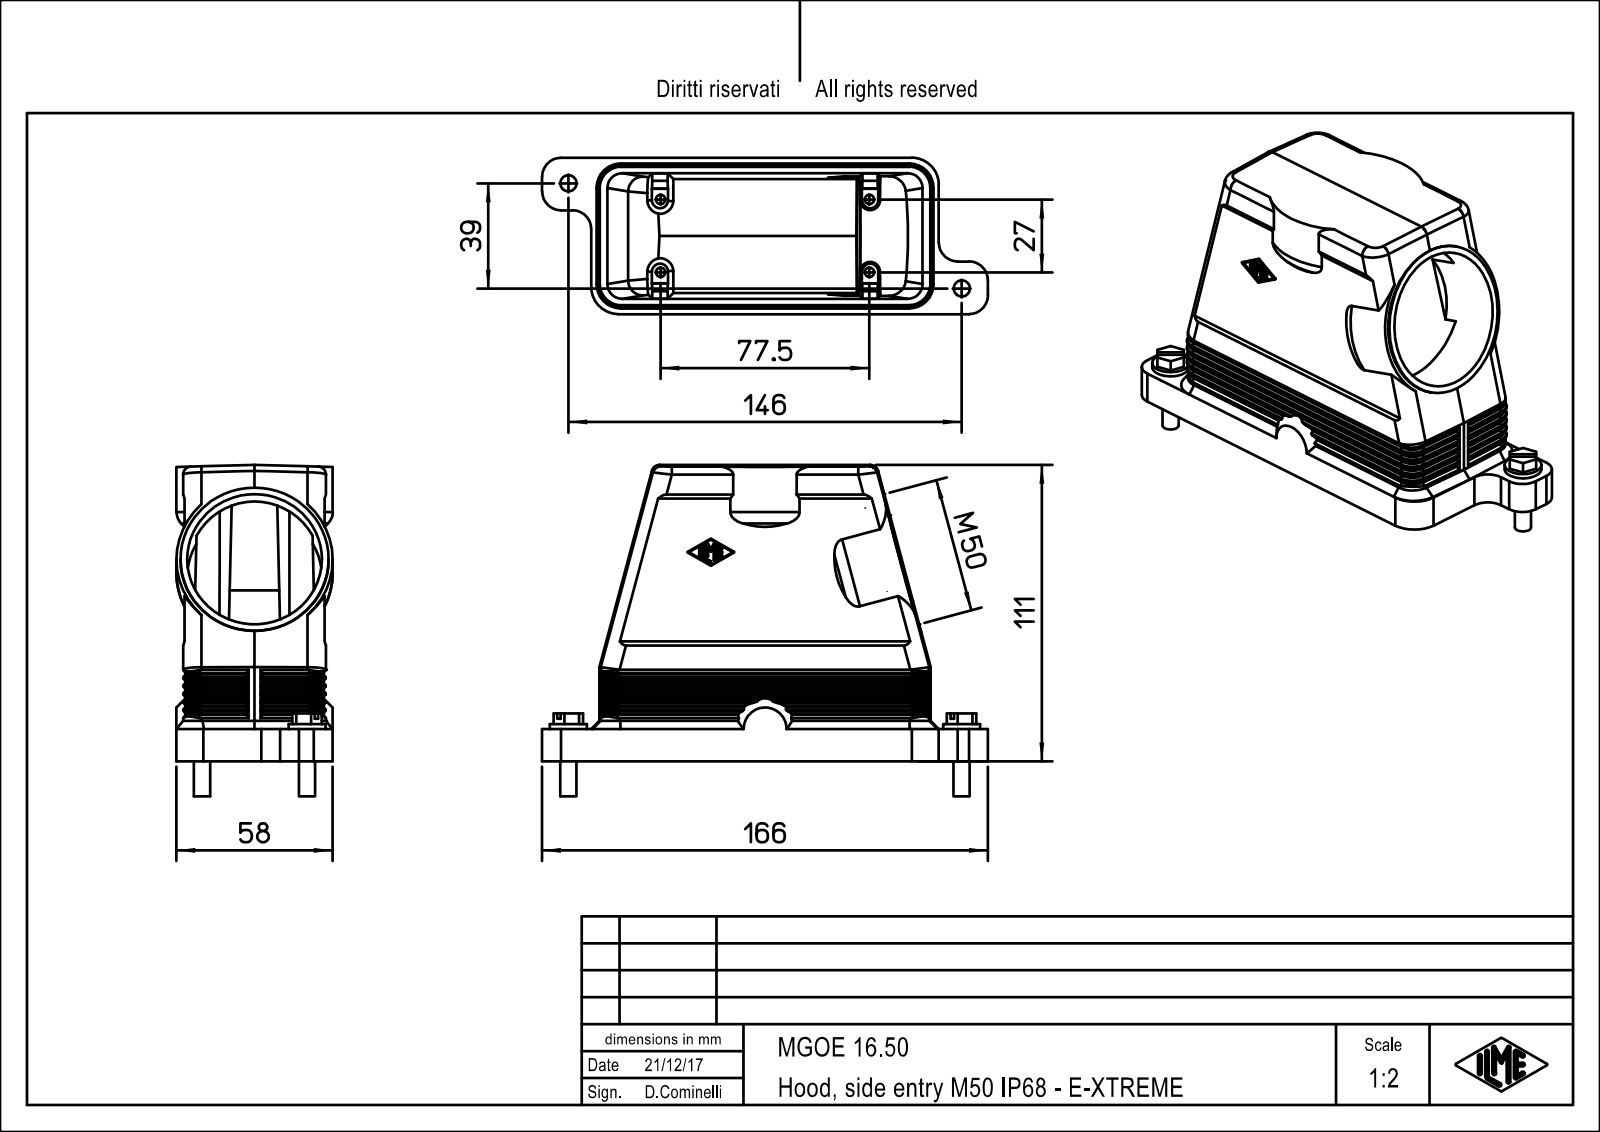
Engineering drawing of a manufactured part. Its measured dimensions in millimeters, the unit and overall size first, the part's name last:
Units: millimetres
Overall size (bounding box): 165.5 × 123 × 58
Round holes (diameter × count): ⌀3.5 ×4, ⌀50 ×1
Round bosses / shafts (diameter × count): ⌀13.7 ×2, ⌀6 ×2, ⌀55 ×1
Partial cylindrical surfaces — rounded edges, fillets, slot ends (radius × count): R7 ×62, R0.33 ×15, R5.5 ×6, R8.5 ×4, R0.17 ×2, R10 ×2, R29 ×2, R0.17 ×1
Main face-to-face distances: 52, 3, 55, 2.5, 0.5, 55.5, 52.5, 3.33, 78, 58
Hole centre spacings: 27, 77.5, 82.07
Volume: 179 654 mm³ · Surface area: 82 541 mm²
Bodies: 1 solid, 537 faces (257 planar, 124 cylindrical, 156 other)
Part name (STEP PRODUCT): MGOE_16.50
STEP written by: PTC Creo Elements/Direct Modeling 19.0E 27-Jun-2016 (C) Parametric Technology GmbH (AUTOMOTIVE_DESIGN)
